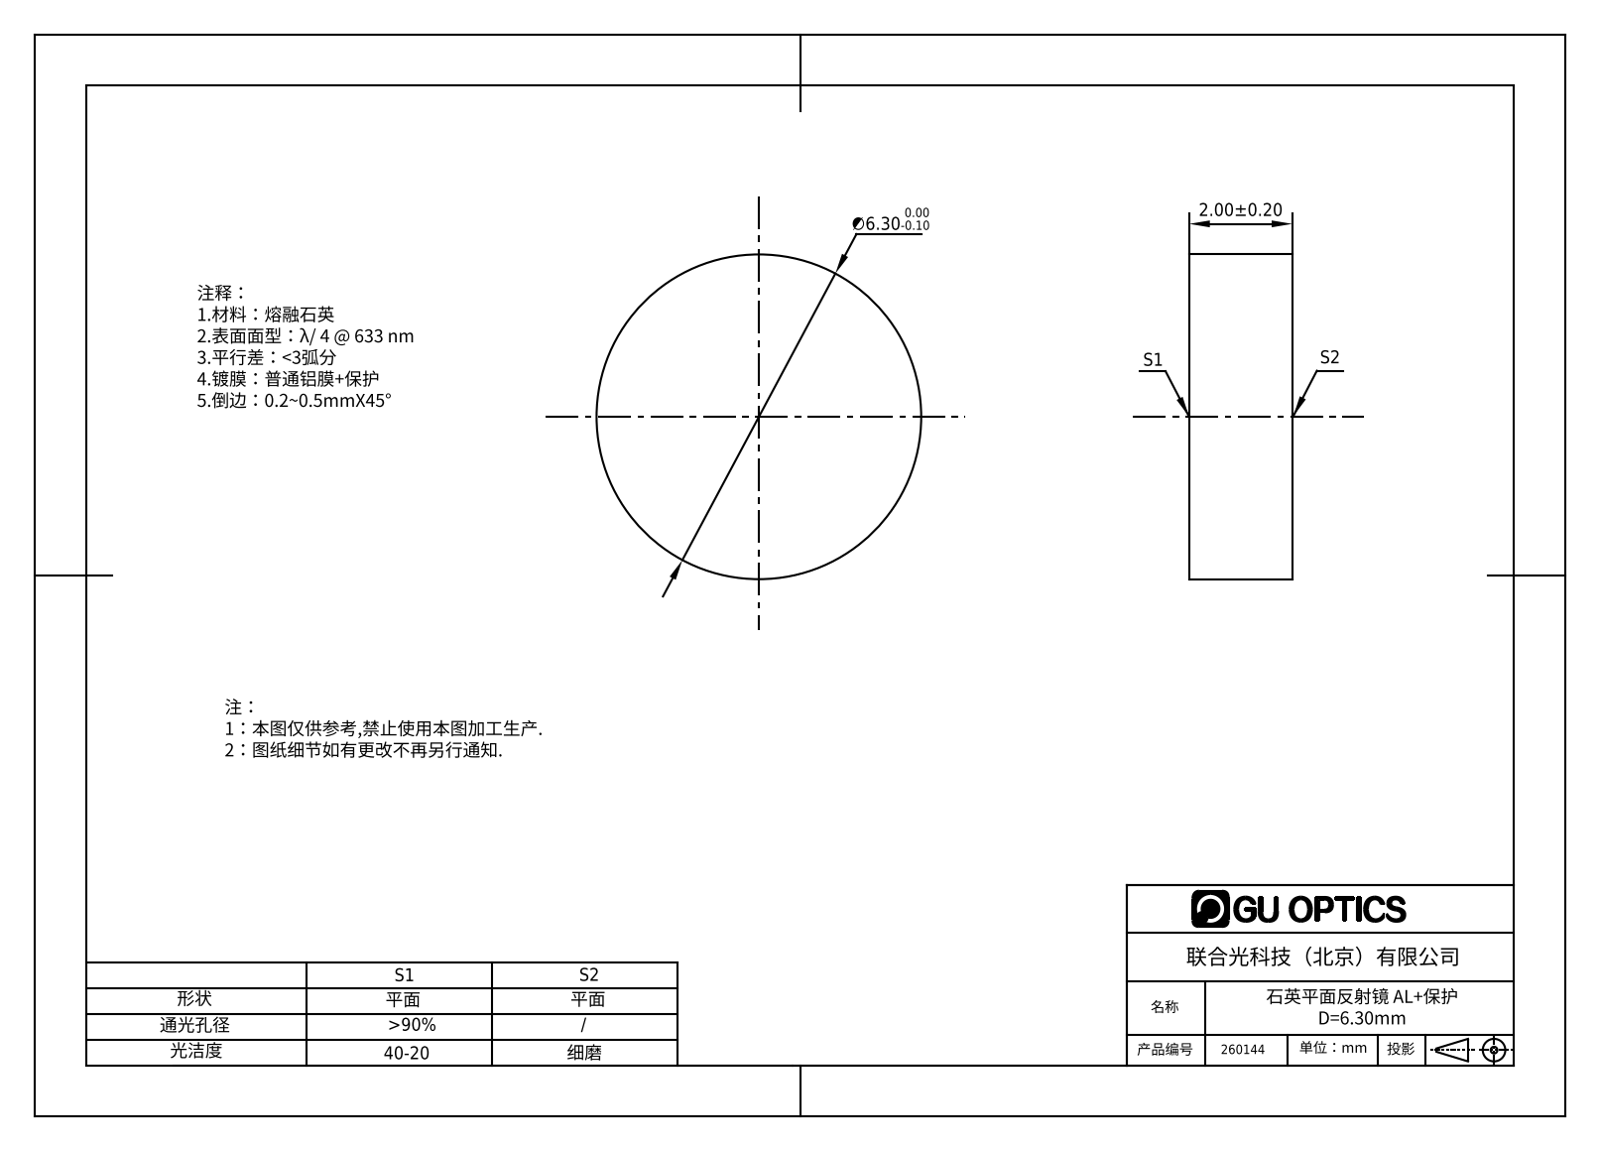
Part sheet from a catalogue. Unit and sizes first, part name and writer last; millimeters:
Units: millimetres
Overall size (bounding box): 6.3 × 6.3 × 2
Round bosses / shafts (diameter × count): ⌀6.3 ×1
Main face-to-face distances: 2
Volume: 62 mm³ · Surface area: 102 mm²
Bodies: 1 solid, 4 faces (2 planar, 2 cylindrical, 0 other)
Part name (STEP PRODUCT): 260001
STEP written by: SolidWorks 2016 (AUTOMOTIVE_DESIGN)
